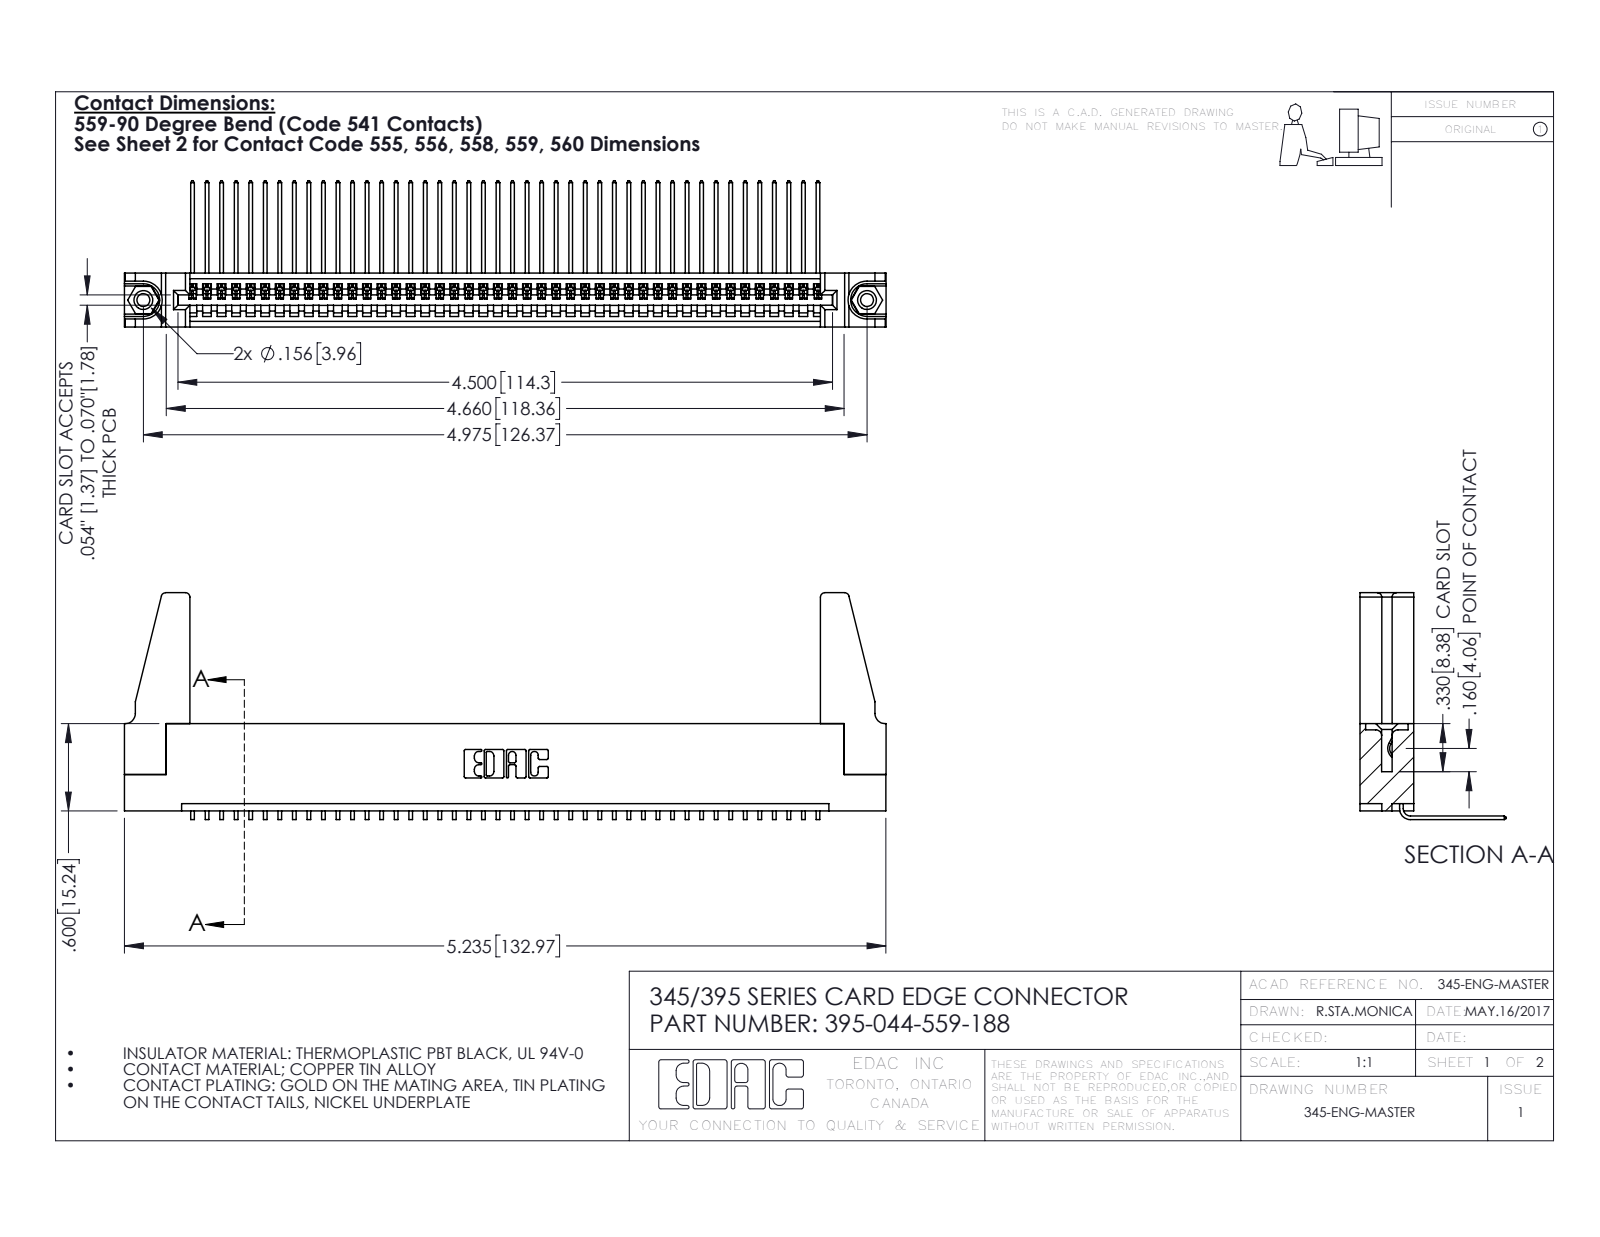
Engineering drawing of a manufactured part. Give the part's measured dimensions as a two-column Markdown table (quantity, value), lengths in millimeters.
| quantity | value |
| --- | --- |
| part name | 345-250-001_345-250-001-102; 345-292-001_558 559 Tail - 1; 345 Part_Flush Mounting Lugs - 0.156 Dia-TH; 345-220-078_345-220-088 (+1 more) |
| STEP written by | SolidWorks 2016 (CONFIG_CONTROL_DESIGN) |
| units | millimeters |
| bodies | 49 solids, 2890 faces (2000 planar, 874 cylindrical, 16 other) |
| overall size | 133 × 39.6 × 25.5 |
| volume | 16 000 mm³ |
| surface area | 21 020 mm² |
| round holes (diameter × count) | 2.3 × 2, 3.2 × 2, 4 × 2, 1.6 × 1 |
| round bosses / shafts (diameter × count) | 3.9 × 2 |
| partial cylindrical surfaces (radius × count) | 0.2 × 88, 0.3 × 22, 0.8 × 8, 0.2 × 6, 0.8 × 6, 0.7 × 3, 0.8 × 2, 1 × 2 |
| main face-to-face distances | 1.8, 7.6, 9.4, 5.1, 2.5, 6.9, 0.6, 5.7, 3.8, 1.8 |
| hole center spacings | 6.9, 120.4, 126.4 |
